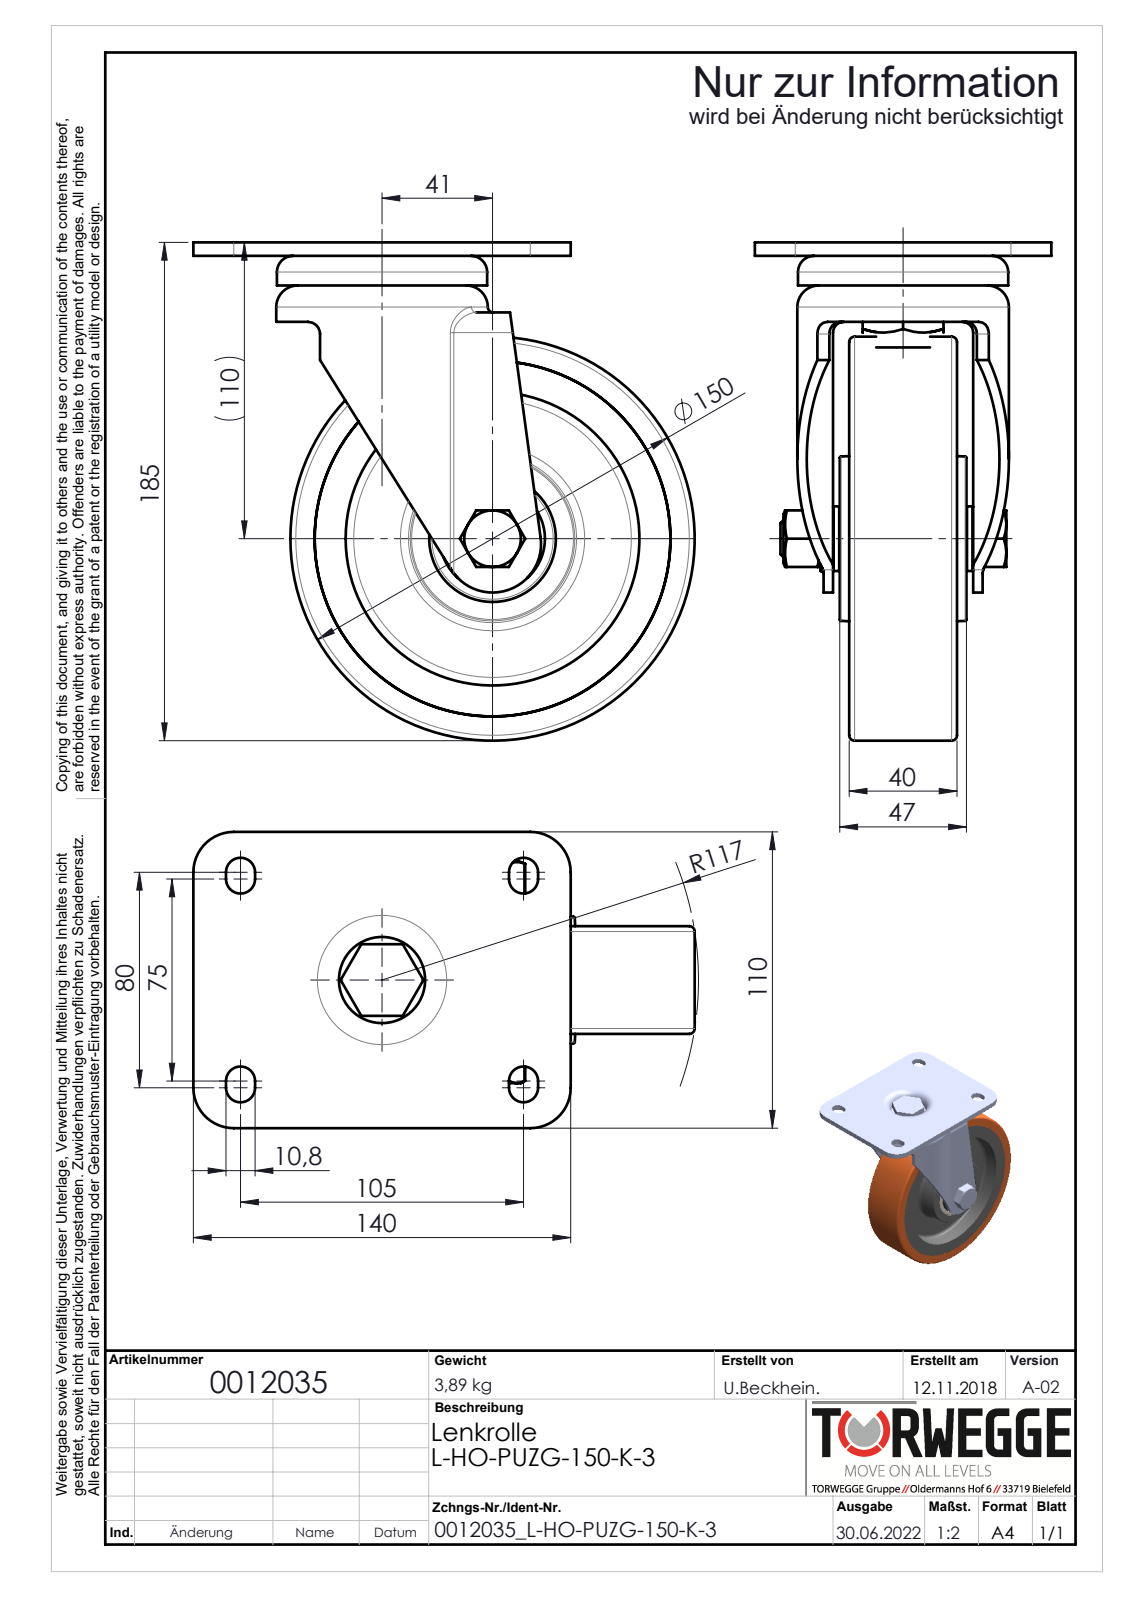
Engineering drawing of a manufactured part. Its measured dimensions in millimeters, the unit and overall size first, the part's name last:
Units: millimetres
Overall size (bounding box): 186 × 185 × 110
Round holes (diameter × count): ⌀12 ×1, ⌀14.2 ×1, ⌀14.5 ×1, ⌀15 ×1, ⌀18.5 ×1, ⌀20 ×1, ⌀20.2 ×1, ⌀30 ×1, ⌀38.9 ×1, ⌀47 ×1, ⌀71.5 ×1, ⌀109 ×1
Round bosses / shafts (diameter × count): ⌀150 ×1, ⌀78.5 ×1, ⌀78 ×1, ⌀28.1 ×1, ⌀25 ×1, ⌀24 ×1, ⌀20 ×1, ⌀14 ×1
Partial cylindrical surfaces — rounded edges, fillets, slot ends (radius × count): R5.4 ×8, R15 ×4, R2 ×2, R4 ×2, R7.5 ×2, R4.5 ×1, R18 ×1
Main face-to-face distances: 3.5, 5, 15, 6, 16, 25, 49.5, 11, 21, 40
Volume: 733 502 mm³ · Surface area: 219 093 mm²
Bodies: 12 solids, 400 faces (134 planar, 119 cylindrical, 147 other)
Part name (STEP PRODUCT): 0012035
STEP written by: SolidWorks 2020 (AUTOMOTIVE_DESIGN)
